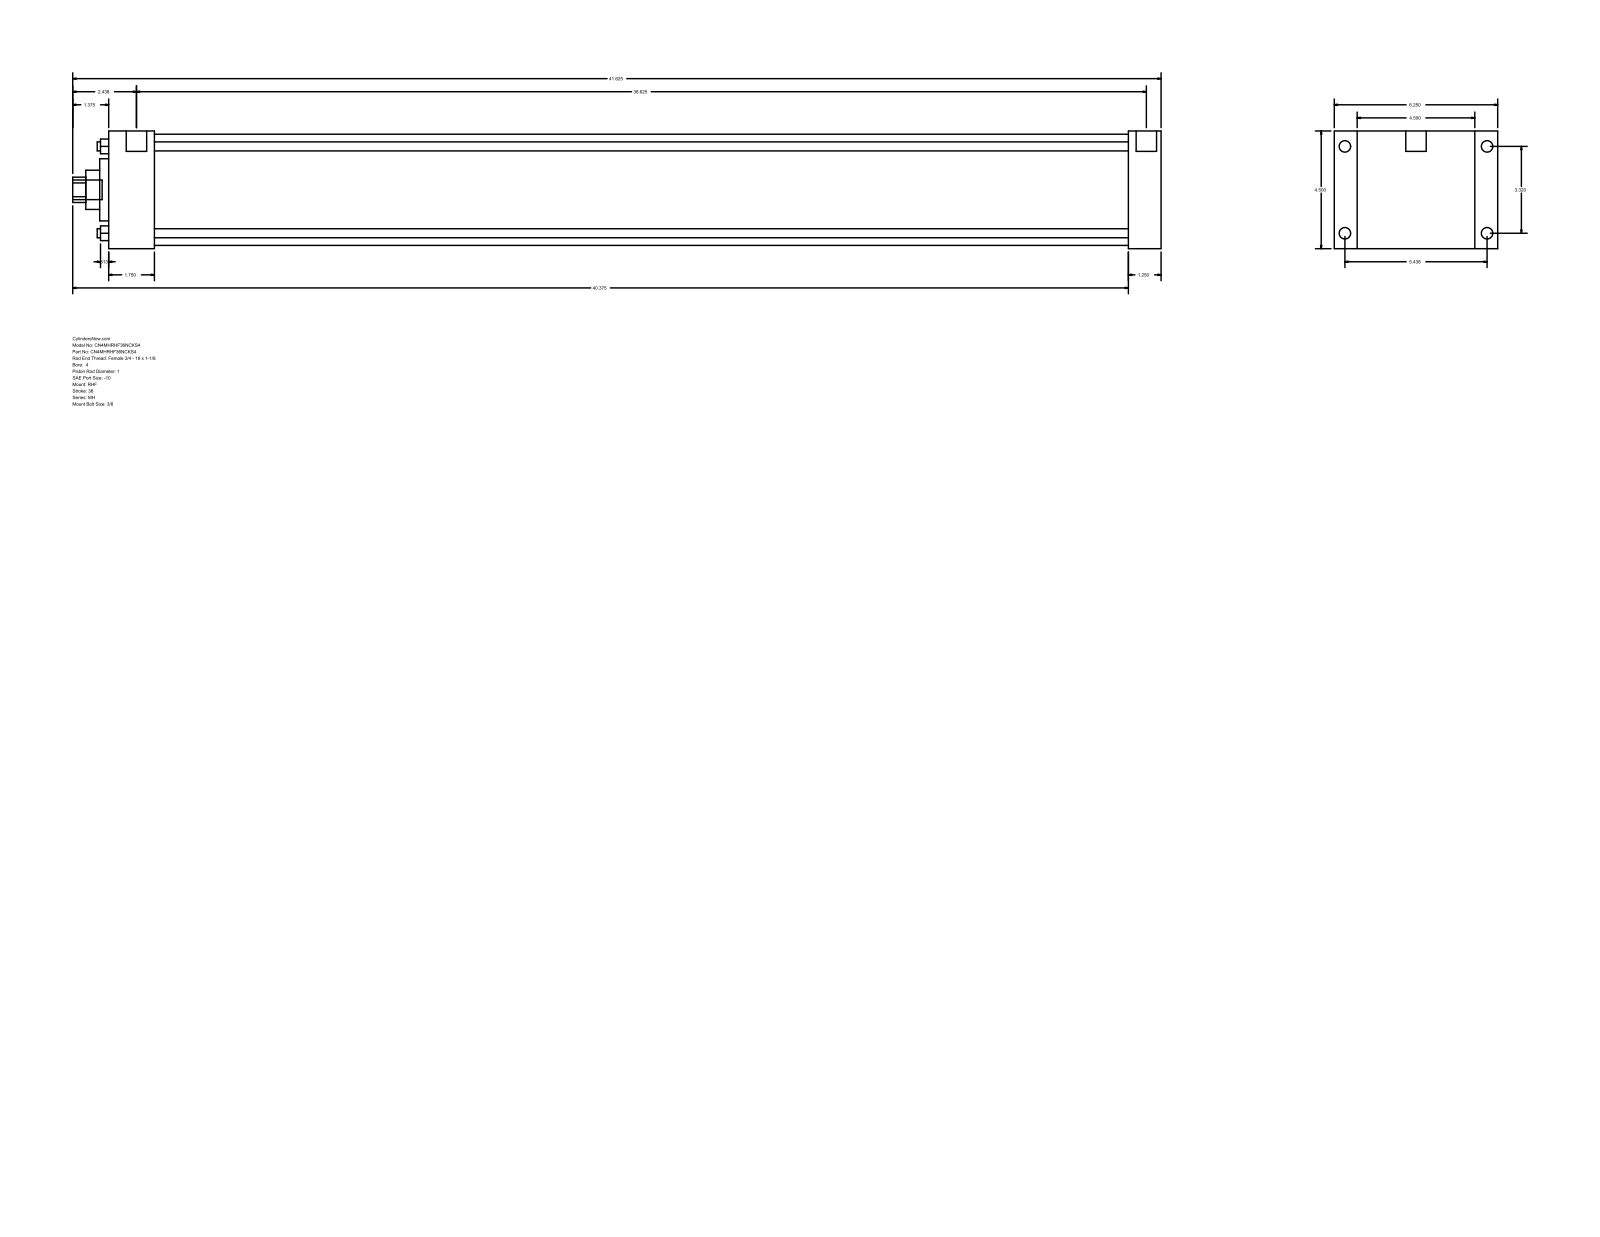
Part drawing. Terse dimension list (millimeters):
name: MH_RHF__0400_1
written by: GSSL Pune (CONFIG_CONTROL_DESIGN)
unit: mm
bodies: 0 solids, 90 faces (61 planar, 29 cylindrical, 0 other)
size: 1057.28 × 158.75 × 114.3
holes: 4× ⌀8.76, 1× ⌀25.4, 1× ⌀38.1, 1× ⌀60.33, 1× ⌀107.95
bosses: 4× ⌀11.13, 4× ⌀8.73, 2× ⌀19.84, 1× ⌀19.05
rounds: 1× R12.29
face distances: 114.3, 1022.36, 990.61, 31.75, 22.23, 136.53, 44.46, 946.15, 977.9, 158.76
hole spacings: 59.62, 84.32, 119.25
